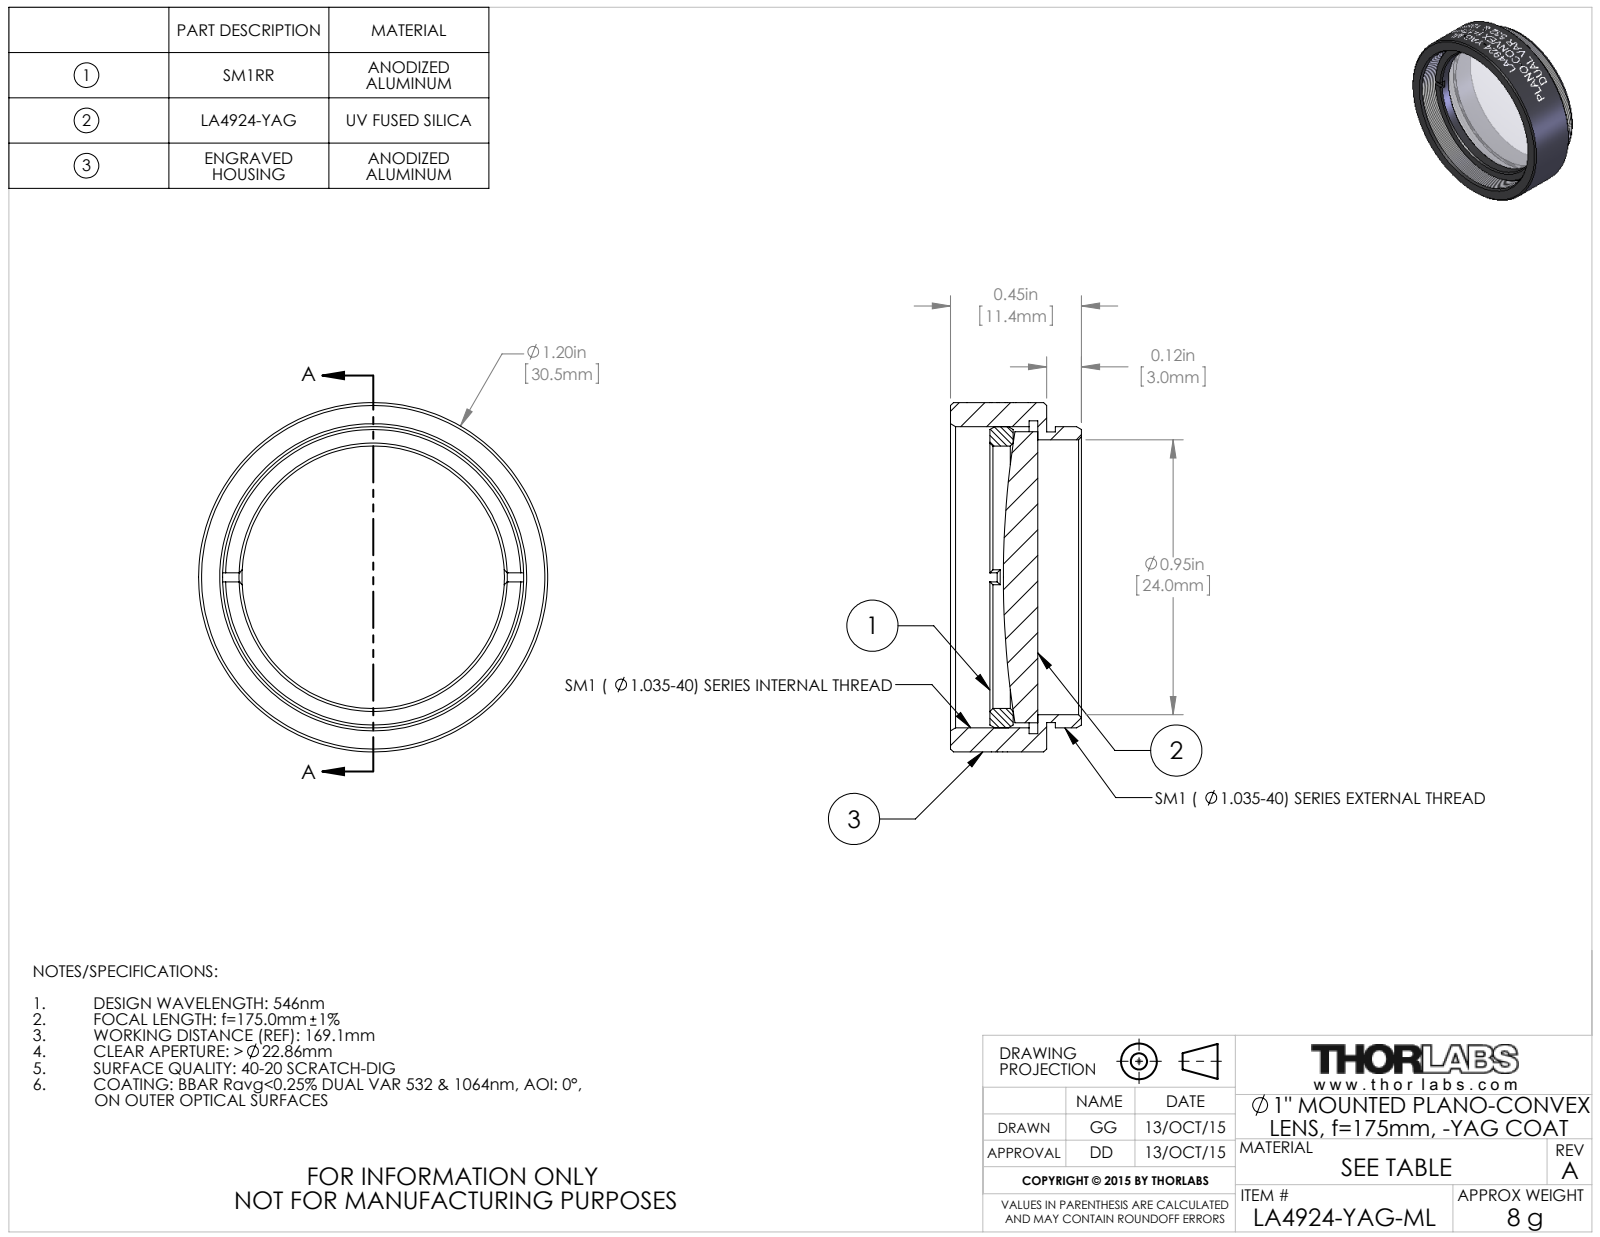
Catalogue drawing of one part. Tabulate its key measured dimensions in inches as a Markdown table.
| quantity | value |
| --- | --- |
| part name | TTN039452-E0W |
| STEP written by | SolidWorks 2014 (CONFIG_CONTROL_DESIGN) |
| units | inches |
| bodies | 3 solids, 153 faces (20 planar, 109 cylindrical, 24 other) |
| overall size | 1.2 × 1.2 × 0.45 |
| volume | 0.205 in³ |
| surface area | 6.69 in² |
| round holes (diameter × count) | 0.902 × 1, 0.945 × 1, 1.075 × 1 |
| round bosses / shafts (diameter × count) | 1.2 × 1, 1.035 × 1, 1 × 1, 0.999 × 1 |
| main face-to-face distances | 0.03, 0.33, 0.3, 0.115, 0.085, 0.215, 0.195, 0.165, 0.08, 0.135 |
